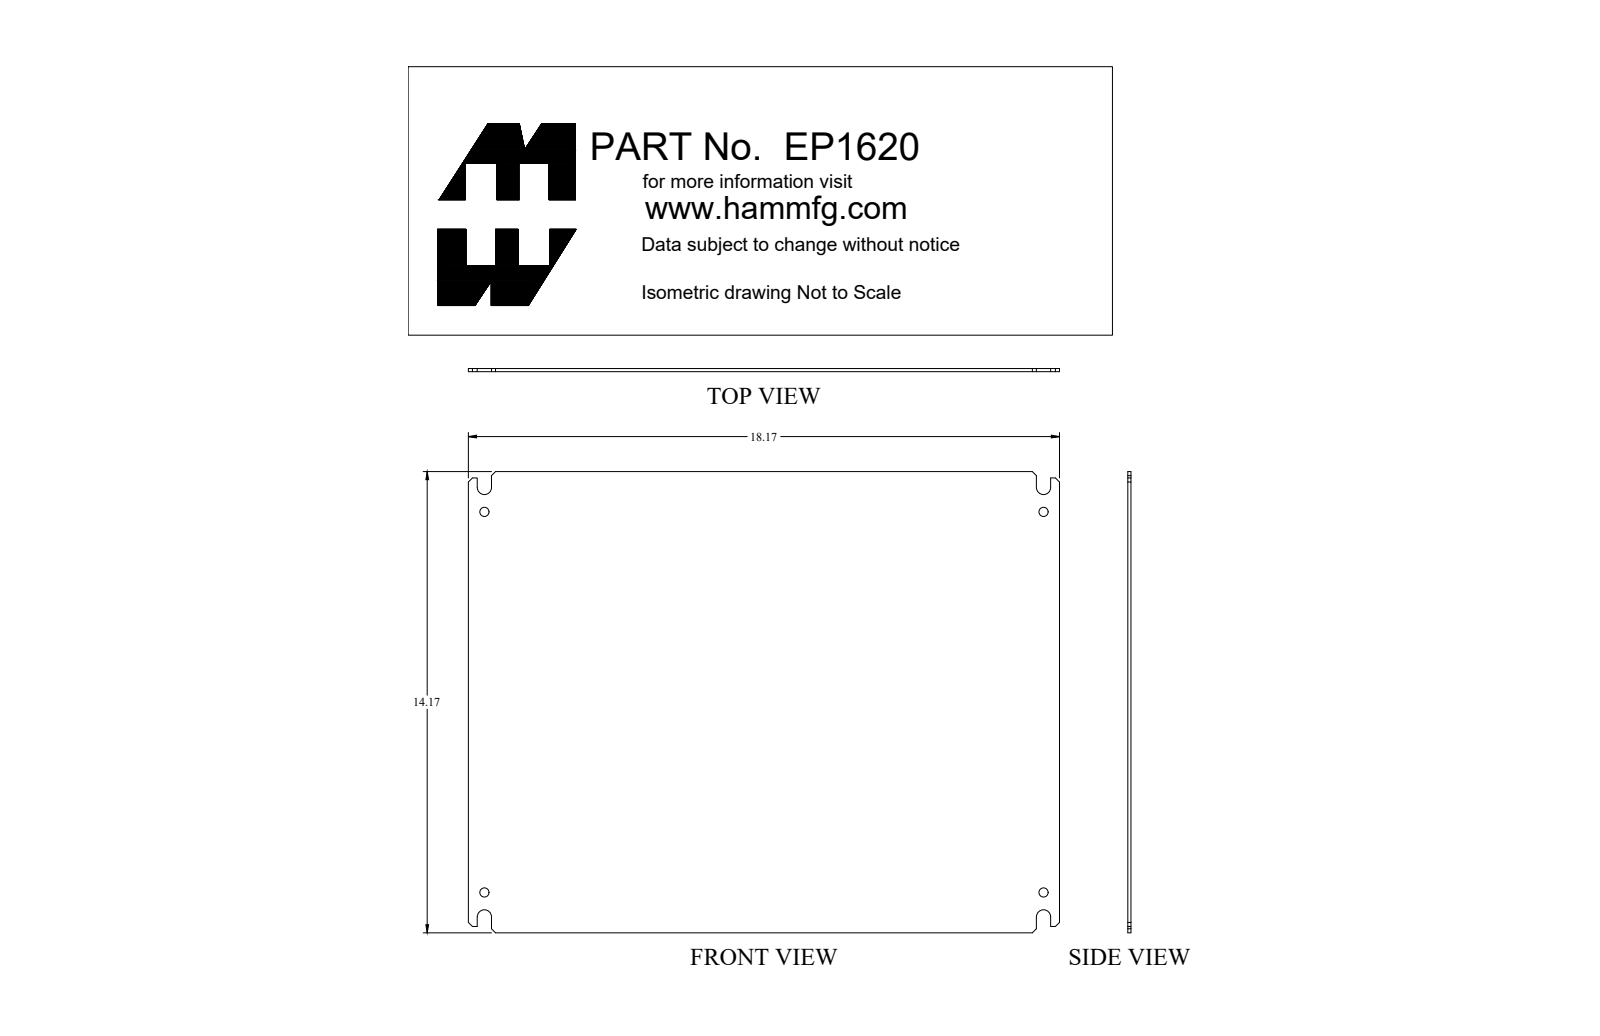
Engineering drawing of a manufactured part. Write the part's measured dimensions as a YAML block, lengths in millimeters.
part_name: "EP1620"
step_written_by: "SolidWorks 2018 (AUTOMOTIVE_DESIGN)"
units: millimeters
bodies: {solids: 1, faces: 40, planar: 26, cylindrical: 14, other: 0}
overall_size: [461.5, 359.9, 2.4]
volume: 398200
surface_area: 334400
round_holes:
  - {diameter: 7.1, count: 4}
partial_cylinders:
  - {radius: 5.6, count: 4}
face_to_face_distances: [2.4, 359.9, 461.5, 18, 443.5, 6.9, 454.6, 11.1, 436.6, 425.5]
hole_center_spacings: [296.9, 436.6, 528]
